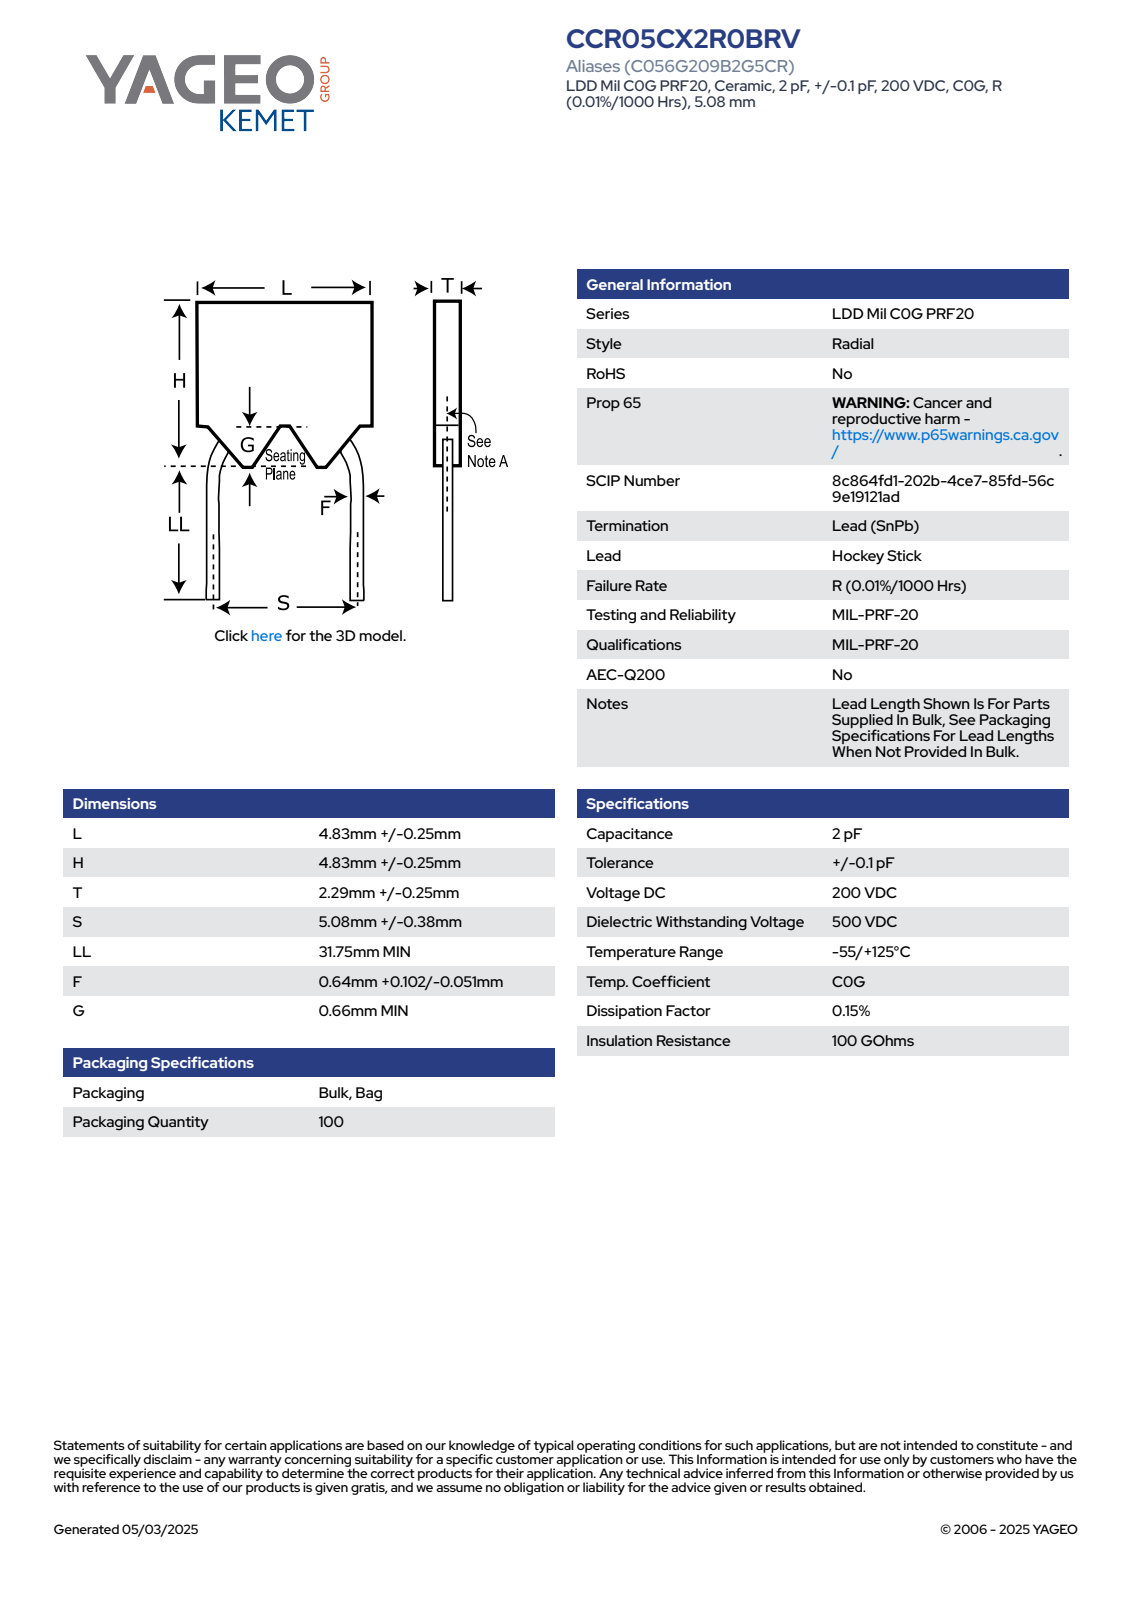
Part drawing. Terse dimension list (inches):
name: CCRM_VHS_C056_L5.08H5.08T2.54S5.08LL31.75F0.64G0.66
written by: SolidWorks 2014 (AUTOMOTIVE_DESIGN)
unit: in
bodies: 4 solids, 85 faces (73 planar, 0 cylindrical, 12 other)
size: 1.45 × 0.223 × 0.1
volume: 0.005 in³; area: 0.352 in²
face distances: 0.1, 0.2, 0.174, 0.058, 0.058, 0.026, 1.25, 1.276, 1.45, 0.03
